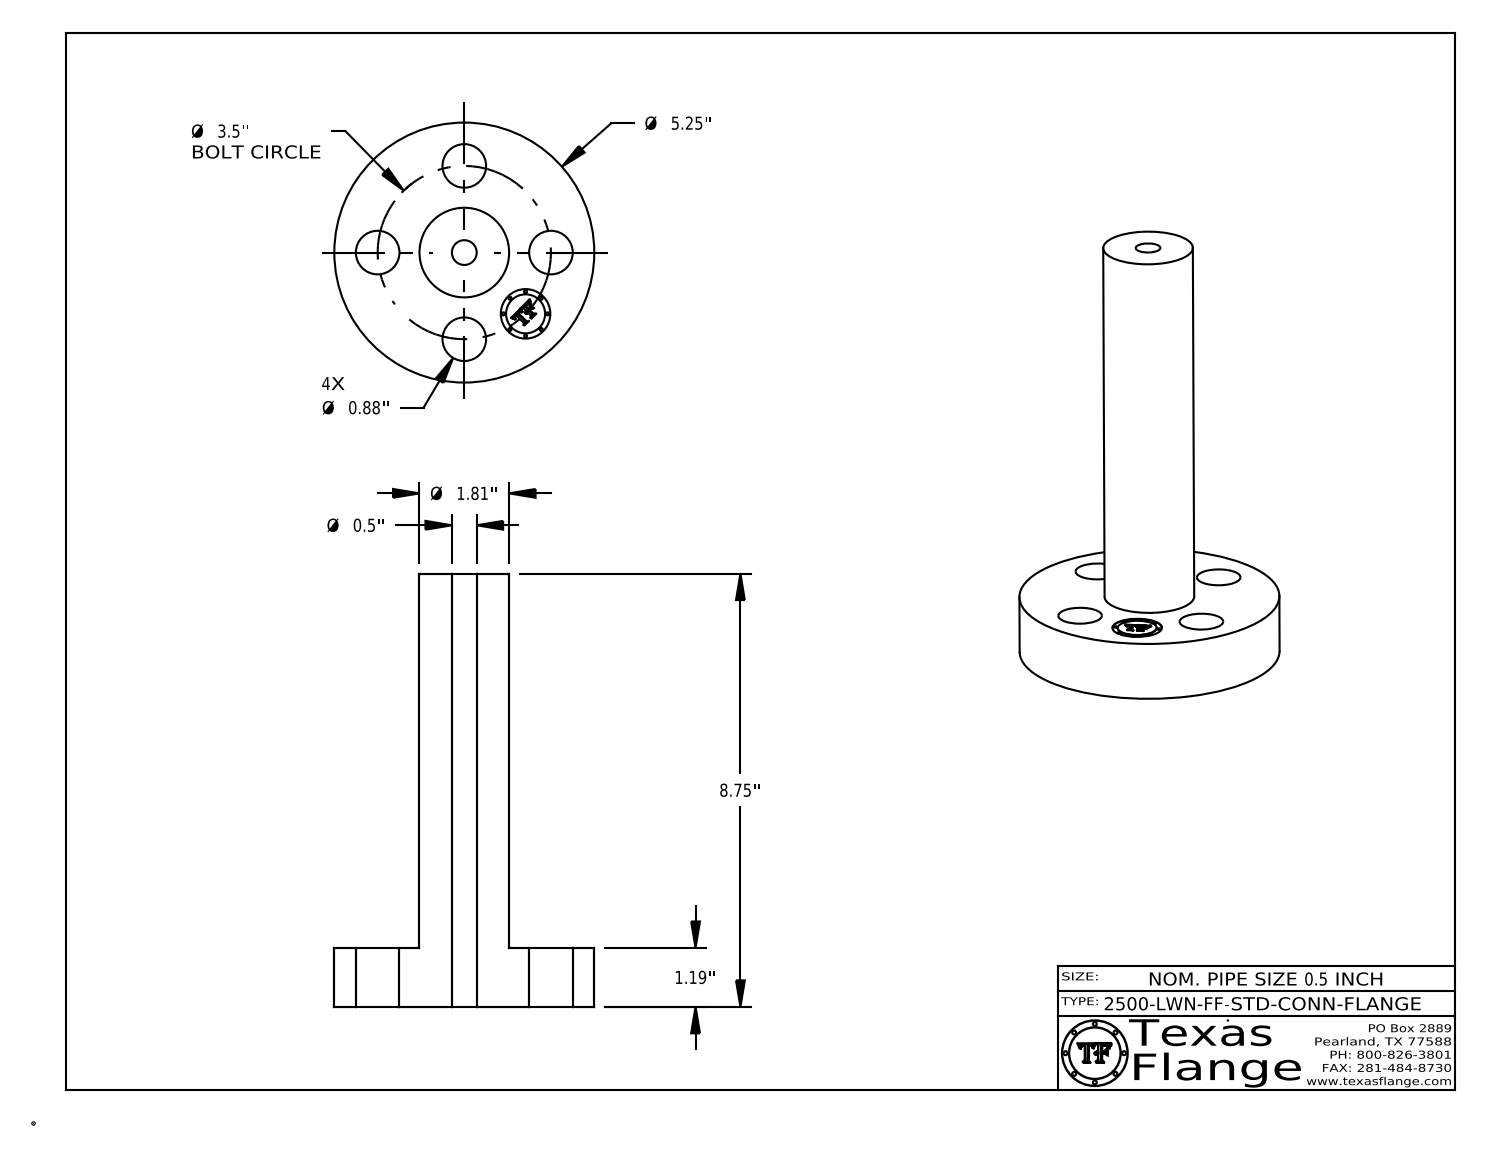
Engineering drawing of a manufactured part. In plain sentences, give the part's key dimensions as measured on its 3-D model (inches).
The part is named "0.5-2500-LWN-FF-STD-CONN-FLANGE". Its 3-D file was written by "CATIA V5 STEP AP214 (AUTOMOTIVE_DESIGN)". It is 1 solid with 402 faces: 368 planar, 34 cylindrical and 0 other. Overall it measures 8.75 by 5.25 by 5.25 inches. Its volume is 40.6 cubic inches and its surface area 127.6 square inches. Round holes: 4 of diameter 0.88, 1 of diameter 0.5, 1 of diameter 1. Round bosses or shafts: 8 of diameter 0.061, 1 of diameter 5.25, 1 of diameter 1.81, 1 of diameter 0.788. The main face-to-face distances are 1.19, 8.75, 7.56, 1.185, 7.565, 0.298, 0.293, 0.054, 0.193, 0.248. The hole center spacings are 1.75, 2.475, 1.339, 3.233, 3.5.
